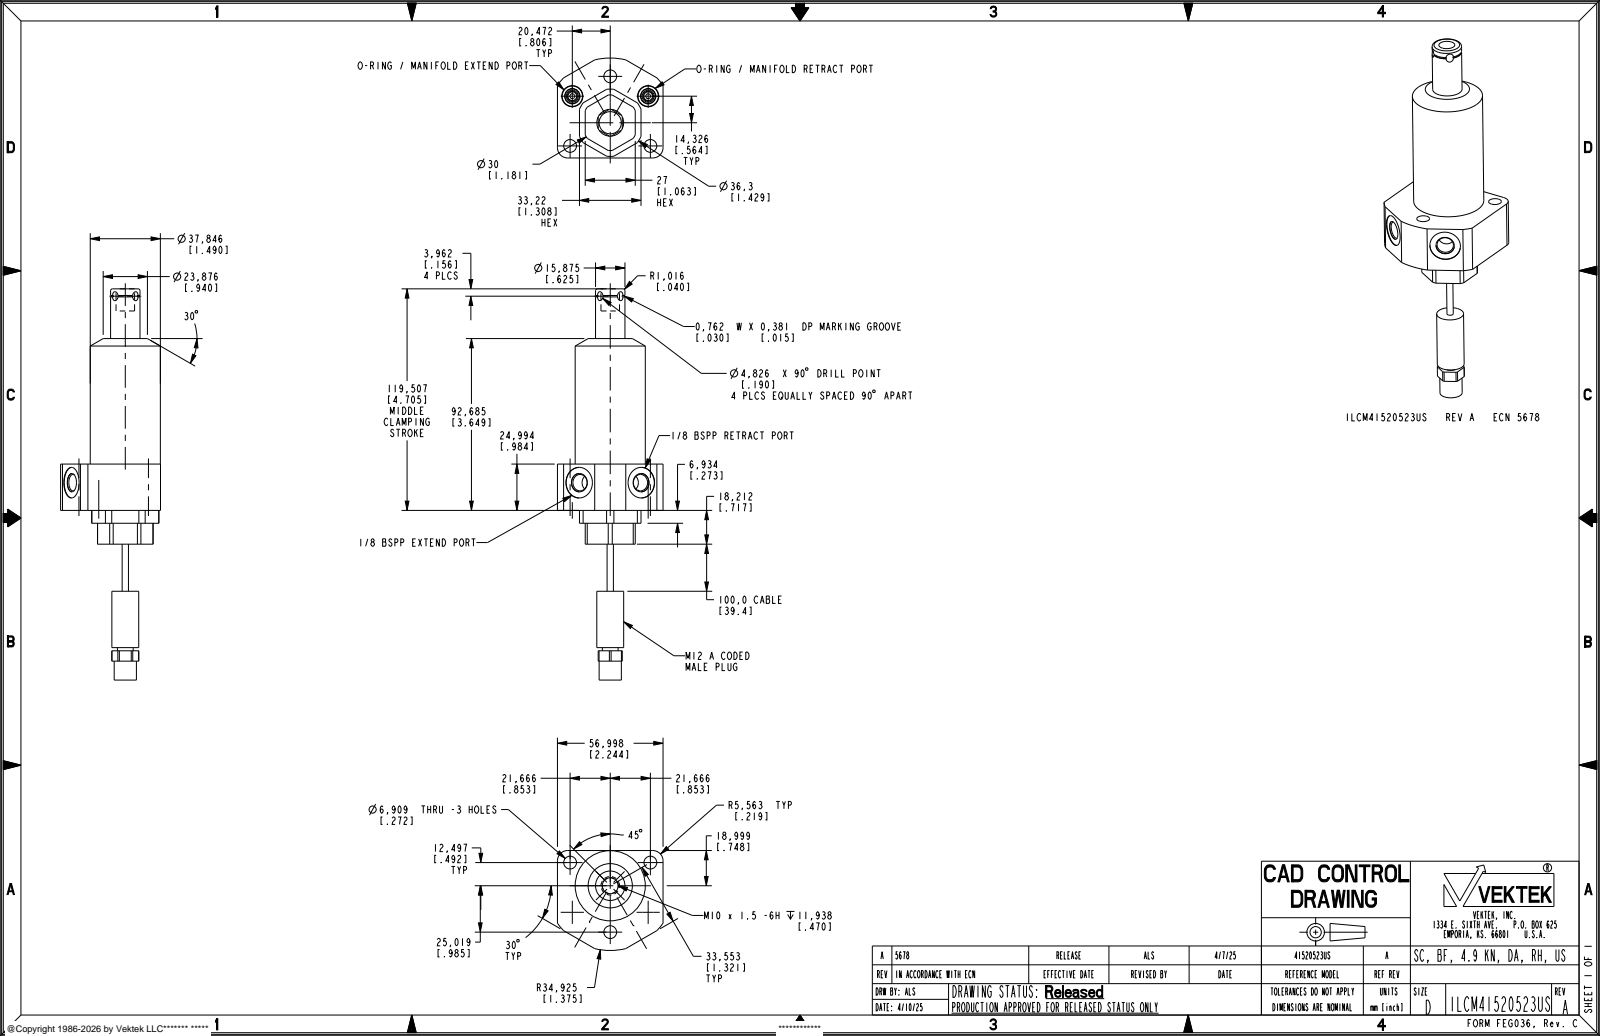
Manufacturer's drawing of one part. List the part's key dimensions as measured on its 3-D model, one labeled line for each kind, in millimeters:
Part name (STEP PRODUCT): ILCM41520523US
STEP written by: CREO PARAMETRIC BY PTC INC, 2021164 (AUTOMOTIVE_DESIGN)
Units: millimetres
Bodies: 1 solid, 184 faces (75 planar, 79 cylindrical, 30 other)
Overall size (bounding box): 211.02 × 69.92 × 65
Volume: 164 674 mm³ · Surface area: 27 750 mm²
Round holes (diameter × count): ⌀6.91 ×3, ⌀2.49 ×2, ⌀6.5 ×2, ⌀8.84 ×2, ⌀9.91 ×2, ⌀11.4 ×2, ⌀16.5 ×2, ⌀8.61 ×1
Round bosses / shafts (diameter × count): ⌀5.49 ×2, ⌀37.85 ×1, ⌀15.88 ×1, ⌀14.5 ×1, ⌀11.99 ×1, ⌀10.01 ×1, ⌀8.51 ×1, ⌀3.4 ×1
Partial cylindrical surfaces — rounded edges, fillets, slot ends (radius × count): R5.56 ×2, R7.56 ×1, R15 ×1, R18.15 ×1, R34.92 ×1
Main face-to-face distances: 24.99, 57, 18.22, 43.21, 3.11, 30.11, 27, 11.28, 6.94, 31.93
Hole centre spacings: 25.02, 23.09, 24.99, 26.86, 43.33, 49.96, 40.94, 43.34
